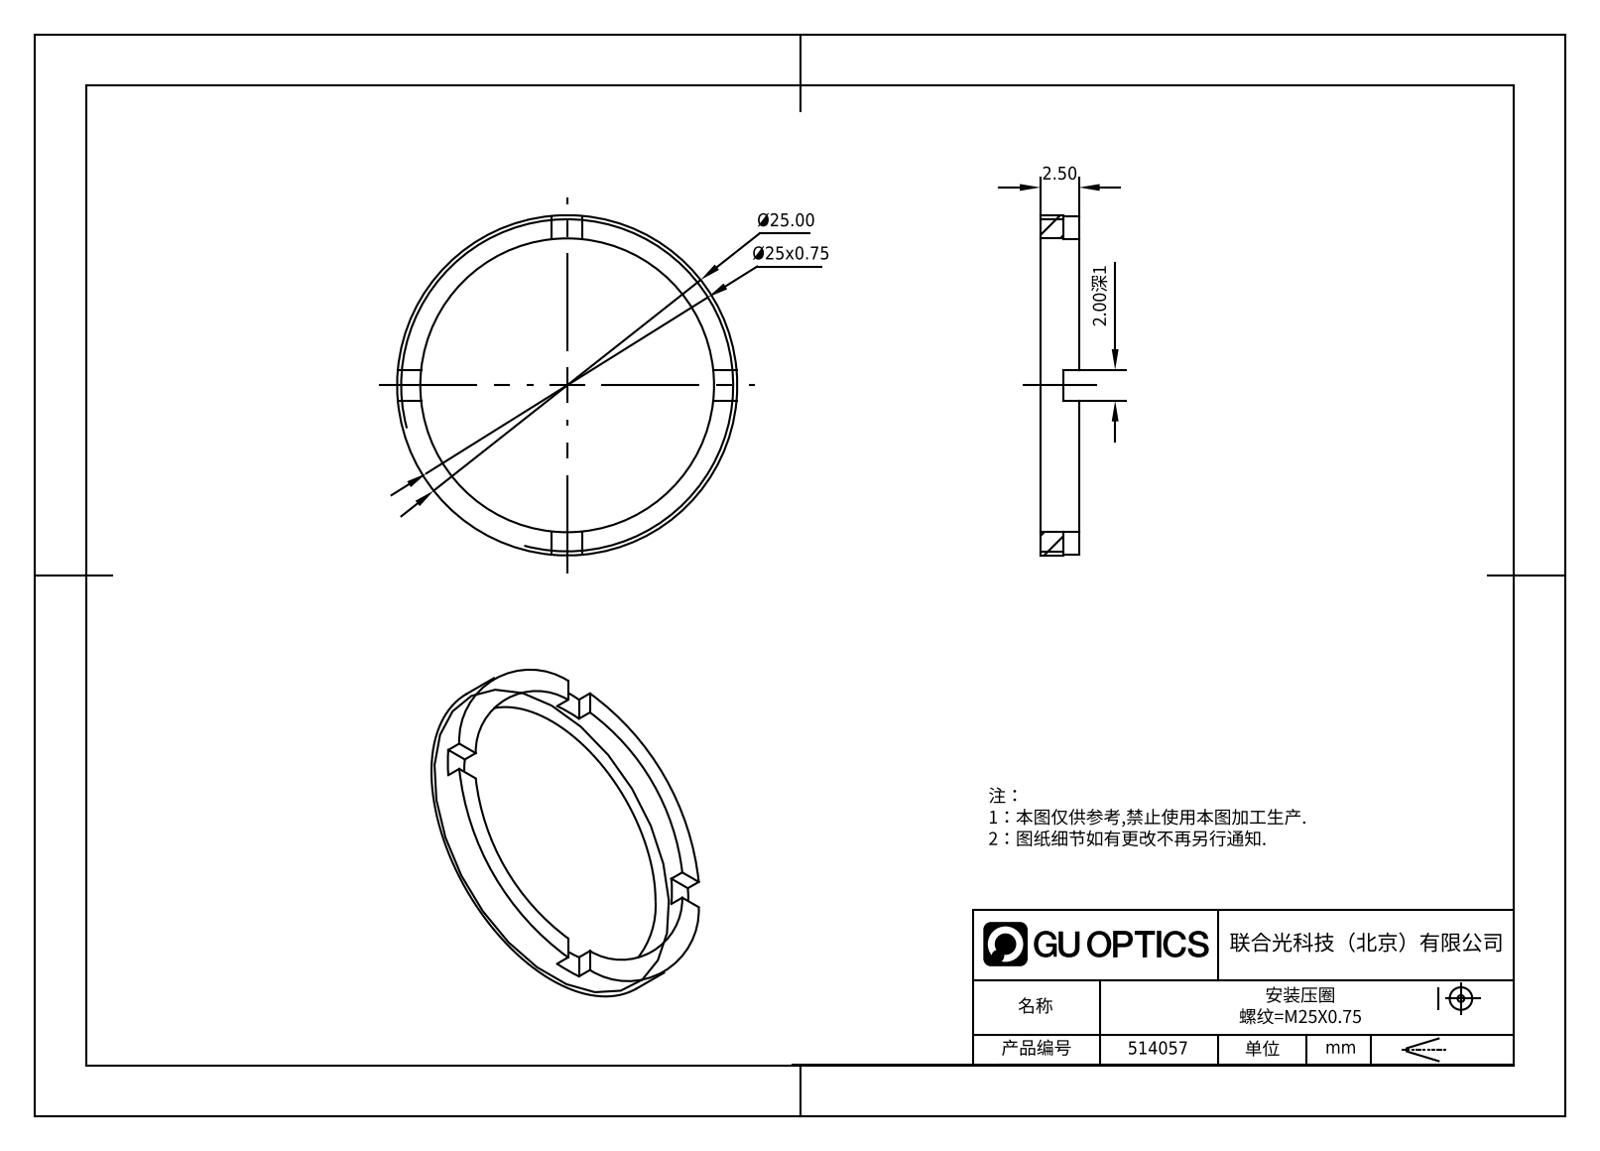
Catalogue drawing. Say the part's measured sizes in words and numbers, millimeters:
The part is named "514057". Its 3-D file was written by "SolidWorks 2020 (CONFIG_CONTROL_DESIGN)". It is 1 solid with 21 faces: 17 planar, 4 cylindrical and 0 other. Overall it measures 25 by 25 by 2.5 millimeters. Its volume is 265 cubic millimeters and its surface area 587 square millimeters. Round holes: 1 of diameter 22. Round bosses or shafts: 1 of diameter 25. The main face-to-face distances are 2.5, 1.5, 1, 2.
